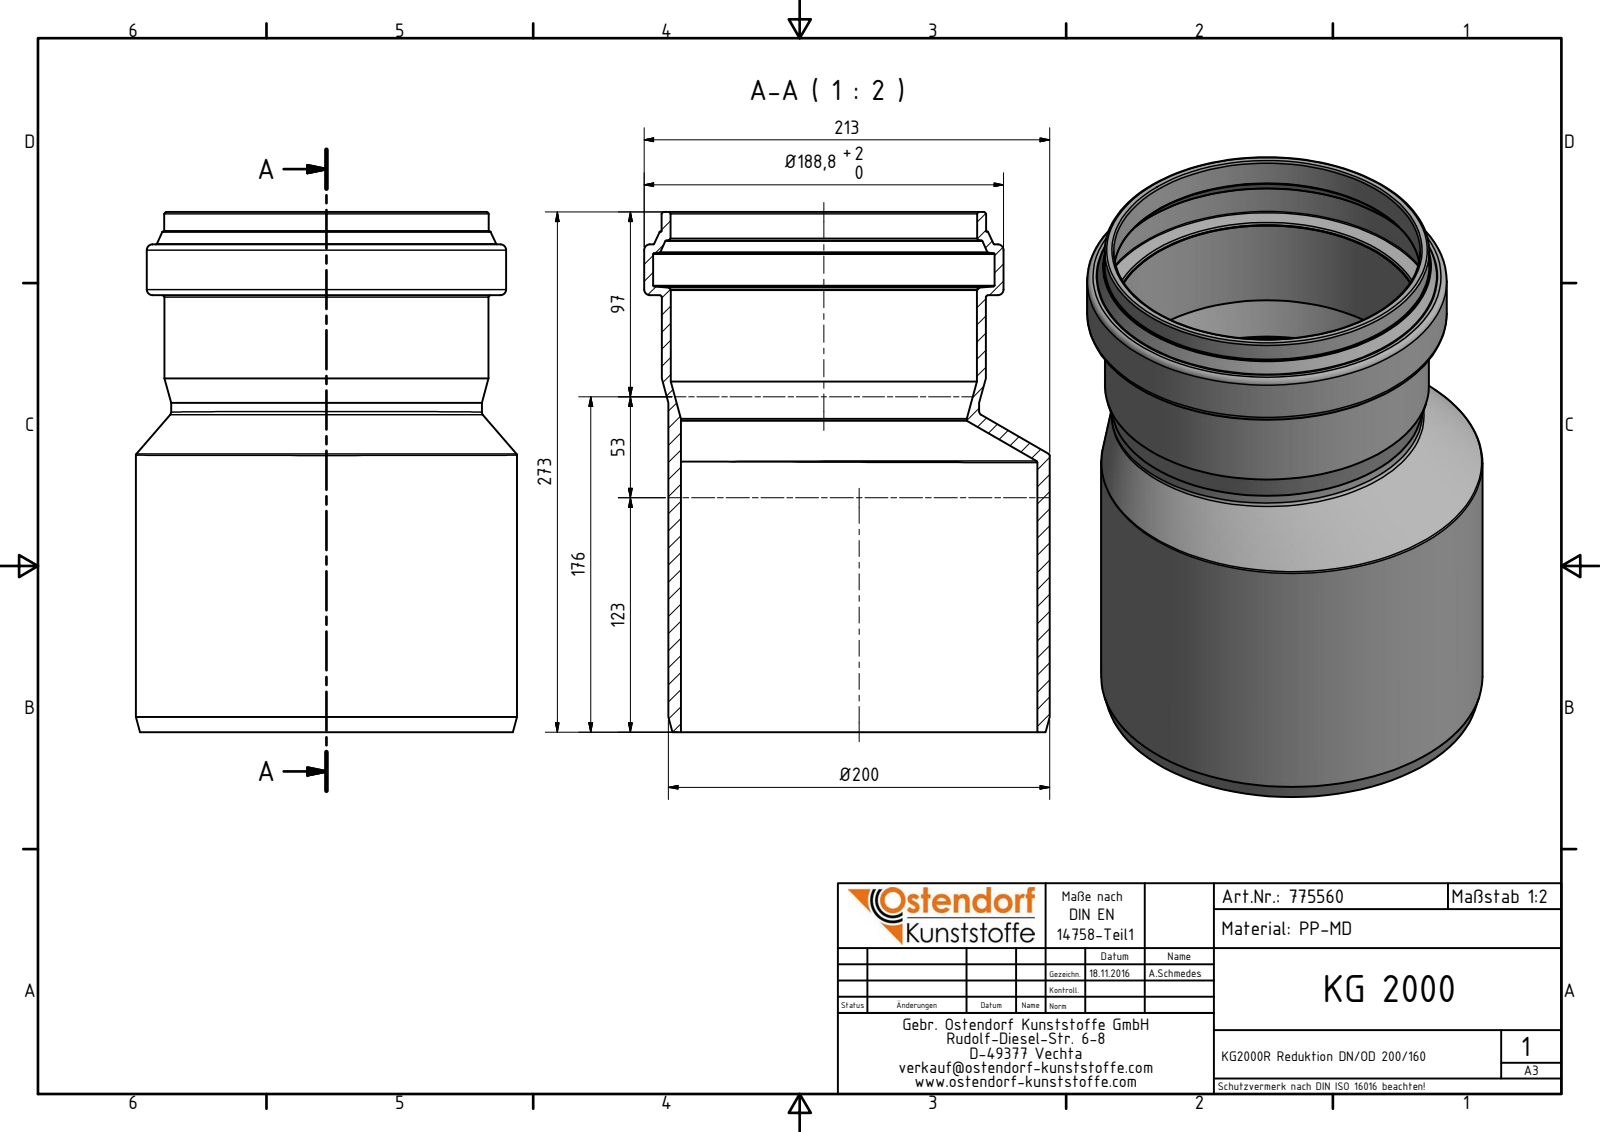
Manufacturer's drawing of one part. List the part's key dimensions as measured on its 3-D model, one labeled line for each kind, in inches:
Part name (STEP PRODUCT): 775560 KG2000R Reduktion DN_OD 200_160
STEP written by: Autodesk Inventor 2016 (AUTOMOTIVE_DESIGN)
Units: inches
Bodies: 1 solid, 44 faces (6 planar, 11 cylindrical, 27 other)
Overall size (bounding box): 10.748 × 8.386 × 7.882
Volume: 59.98 in³ · Surface area: 530.7 in²
Round holes (diameter × count): ⌀5.913 ×1, ⌀6.327 ×1, ⌀6.339 ×1, ⌀7.063 ×1, ⌀7.37 ×1
Round bosses / shafts (diameter × count): ⌀7.882 ×1, ⌀7.433 ×1, ⌀6.709 ×1, ⌀6.697 ×1, ⌀6.425 ×1
Main face-to-face distances: 9.028, 10.748, 1.72, 10.079, 1.051, 0.669, 10.343, 1.315, 0.264, 0.406
Hole centre spacings: 0.728
